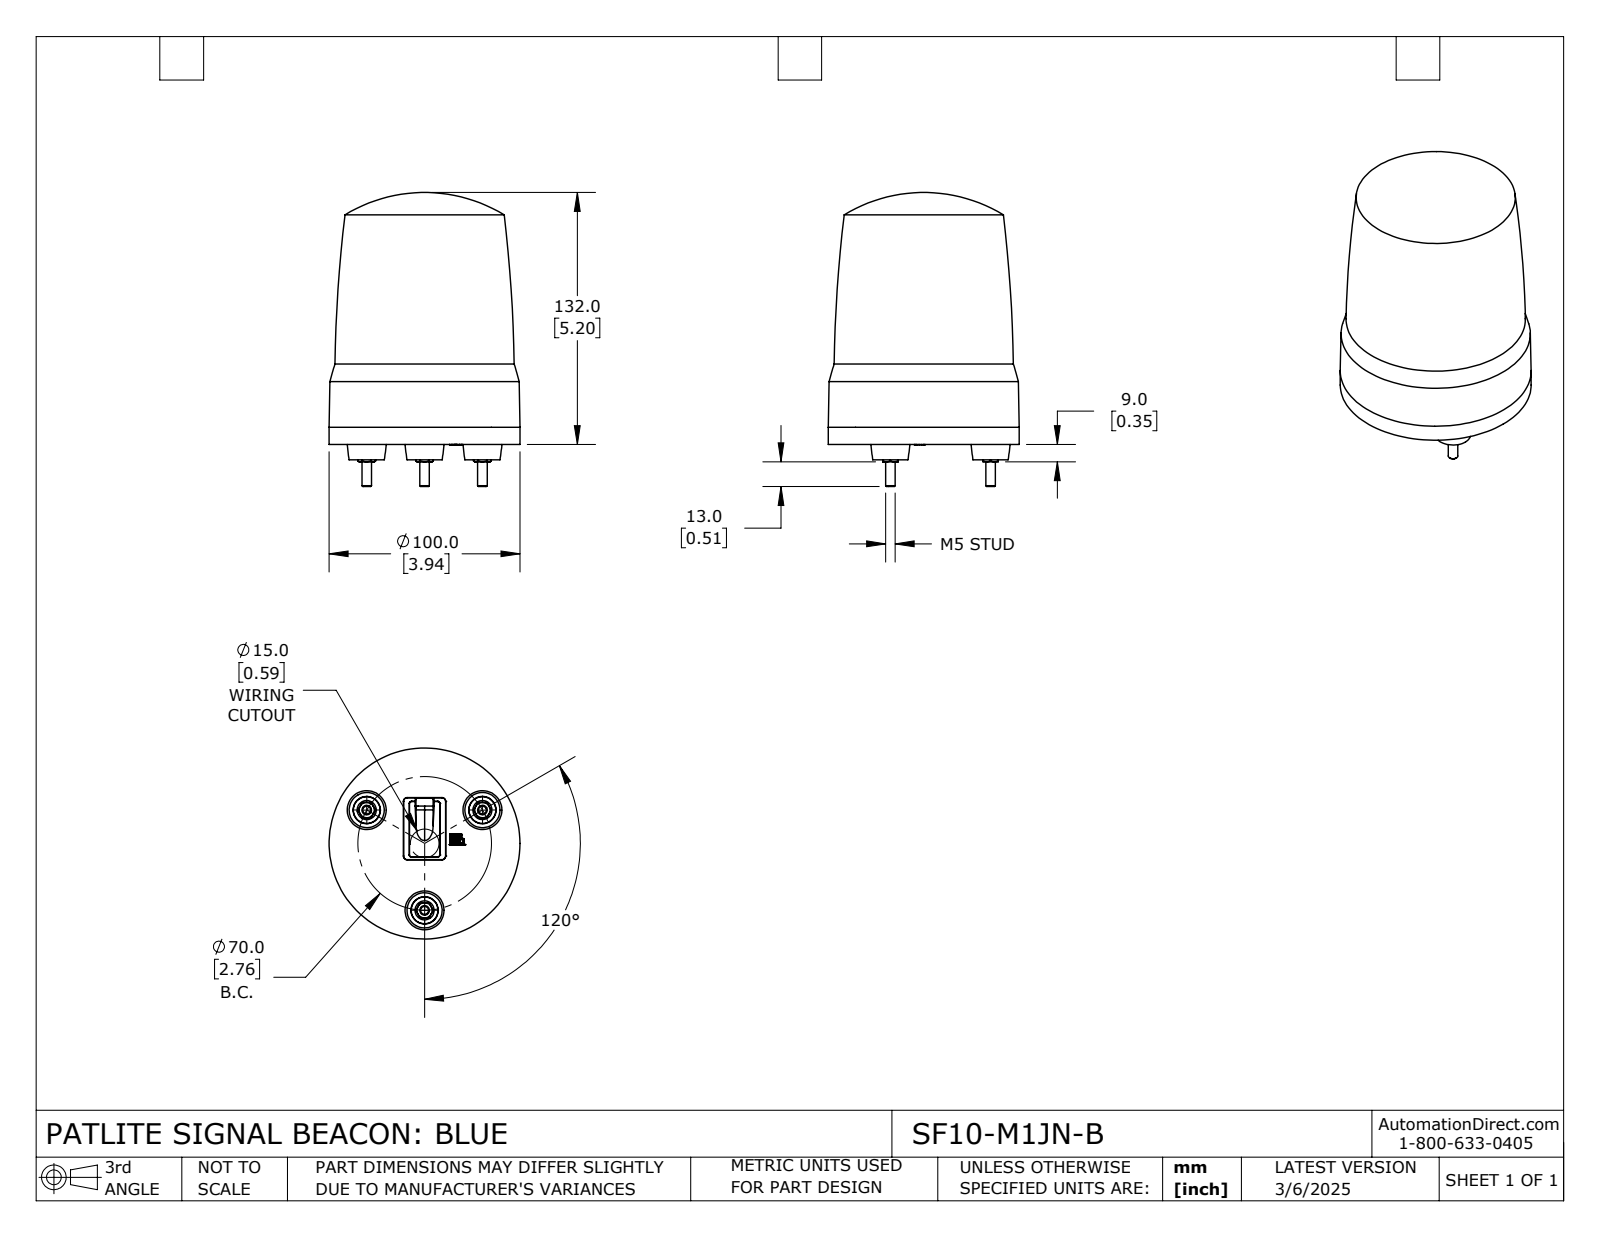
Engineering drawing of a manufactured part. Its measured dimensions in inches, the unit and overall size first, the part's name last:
Units: inches
Overall size (bounding box): 6.063 × 3.937 × 3.937
Round bosses / shafts (diameter × count): ⌀0.394 ×3, ⌀0.197 ×3, ⌀3.937 ×1
Main face-to-face distances: 0.315, 0.033, 0.348, 0.063, 0.411, 0.096, 0.15, 0.165, 0.199, 0.262
Volume: 52.48 in³ · Surface area: 81.51 in²
Bodies: 1 solid, 327 faces (159 planar, 14 cylindrical, 154 other)
Part name (STEP PRODUCT): SF10-M1JN-B
STEP written by: SolidWorks 2024 (CONFIG_CONTROL_DESIGN)
